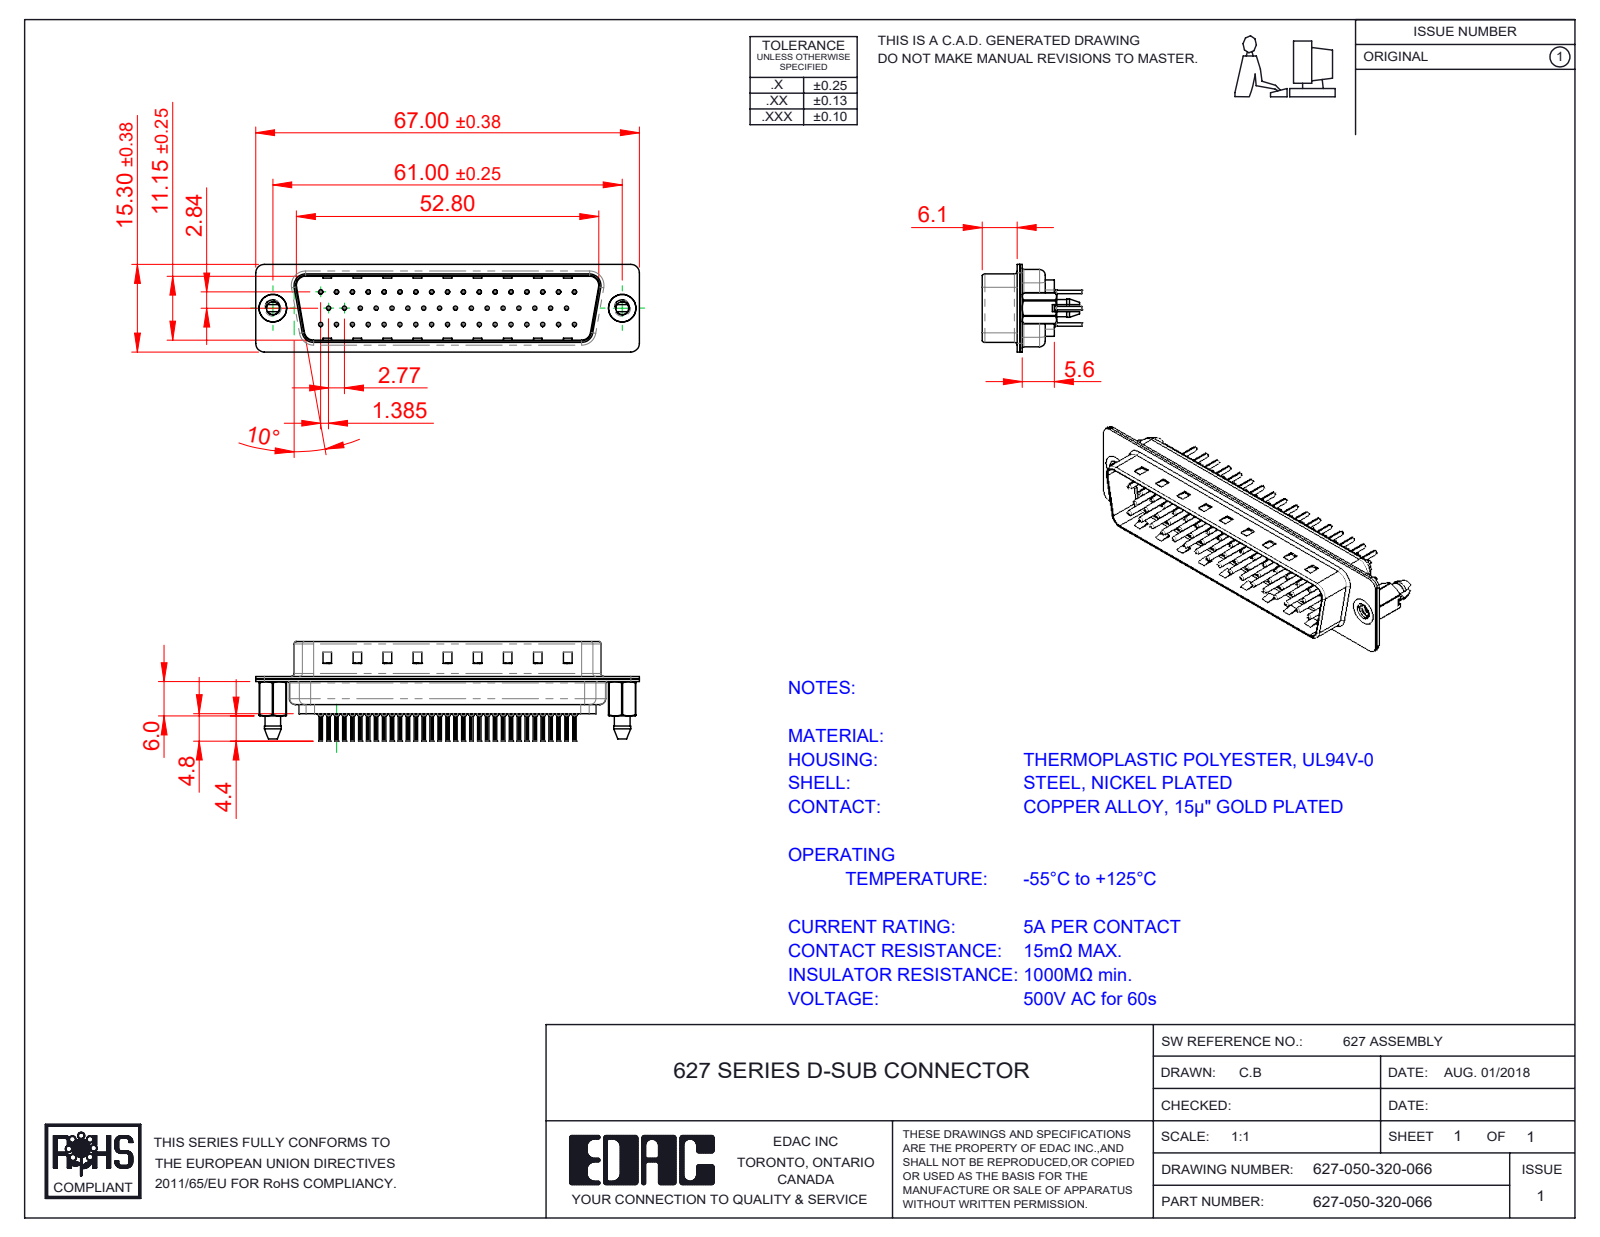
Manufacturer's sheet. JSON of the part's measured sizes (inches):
{"part_name": "627 Housing_50 LP; 627 Contact Row 1_20L; 627-050-320-066; 627 Contact Row 3_20L (+4 more)", "step_written_by": "SolidWorks 2020 (CONFIG_CONTROL_DESIGN)", "units": "inches", "bodies": {"solids": 55, "faces": 5386, "planar": 1435, "cylindrical": 2023, "other": 1928}, "overall_size": [2.638, 0.681, 0.602], "volume_in3": 0.277, "surface_area_in2": 19.96, "round_holes": [[0.008, 50], [0.014, 50], [0.043, 50], [0.063, 50], [0.089, 2], [0.157, 2], [0.189, 2]], "round_bosses_or_shafts": [[0.079, 50], [0.059, 50], [0.03, 50], [0.024, 50], [0.193, 2]], "partial_cylinders_radius": [[0.004, 100], [0.059, 18], [0.079, 12], [0.063, 10], [0.02, 8], [0.01, 4], [0.024, 4], [0.026, 4]], "face_to_face_distances": [0.016, 0.018, 0.455, 0.238, 0.035, 0.256, 0.031, 0.485, 0.077, 0.03], "hole_center_spacings": [0.124, 0.109, 0.218, 0.327, 0.436, 0.545, 0.654, 0.198]}
